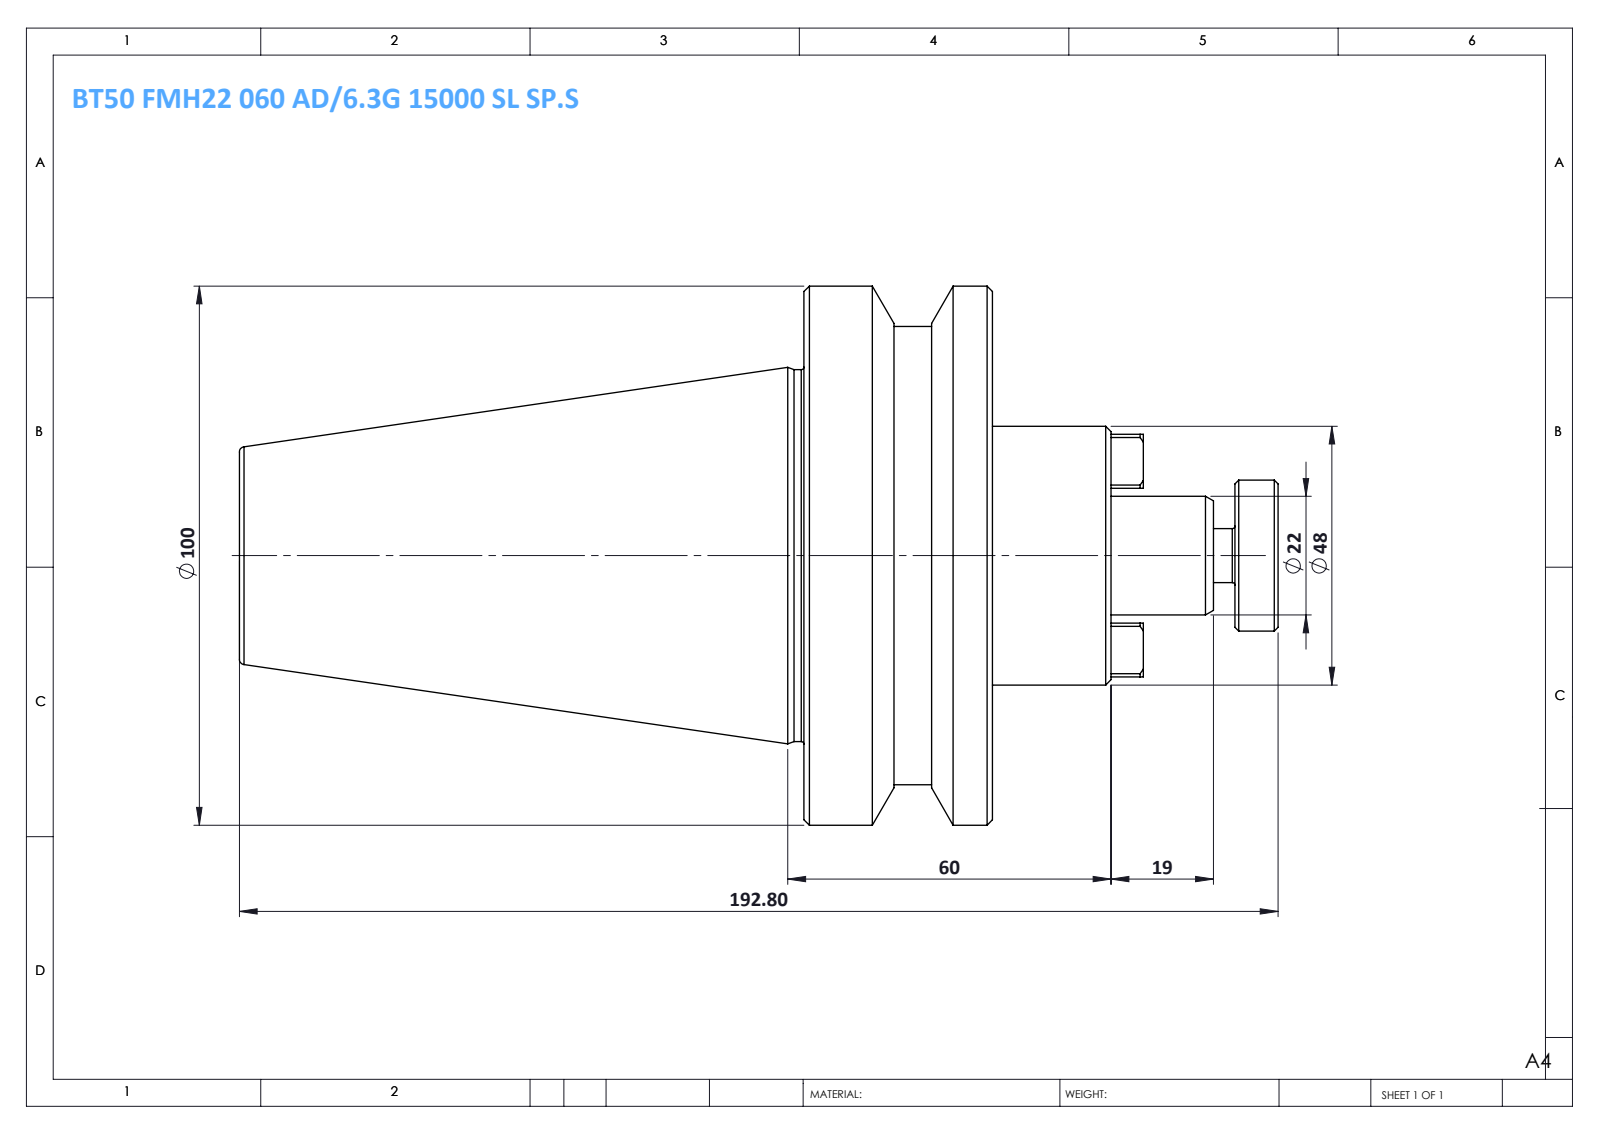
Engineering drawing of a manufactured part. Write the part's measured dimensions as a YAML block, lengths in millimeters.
part_name: "BT50 FMH22 060 AD-6.3G 15000 SL SP.S"
step_written_by: "SolidWorks 2014 (CONFIG_CONTROL_DESIGN)"
units: millimeters
bodies: {solids: 1, faces: 77, planar: 35, cylindrical: 16, other: 26}
overall_size: [192.8, 100, 100]
volume: 563398
surface_area: 51143
round_bosses_or_shafts:
  - {diameter: 100, count: 1}
  - {diameter: 85, count: 1}
  - {diameter: 69, count: 1}
  - {diameter: 48, count: 1}
  - {diameter: 28, count: 1}
  - {diameter: 22, count: 1}
  - {diameter: 10, count: 1}
face_to_face_distances: [35, 139.8, 104.8, 22, 57, 161.8, 31, 53, 88, 192.8]
